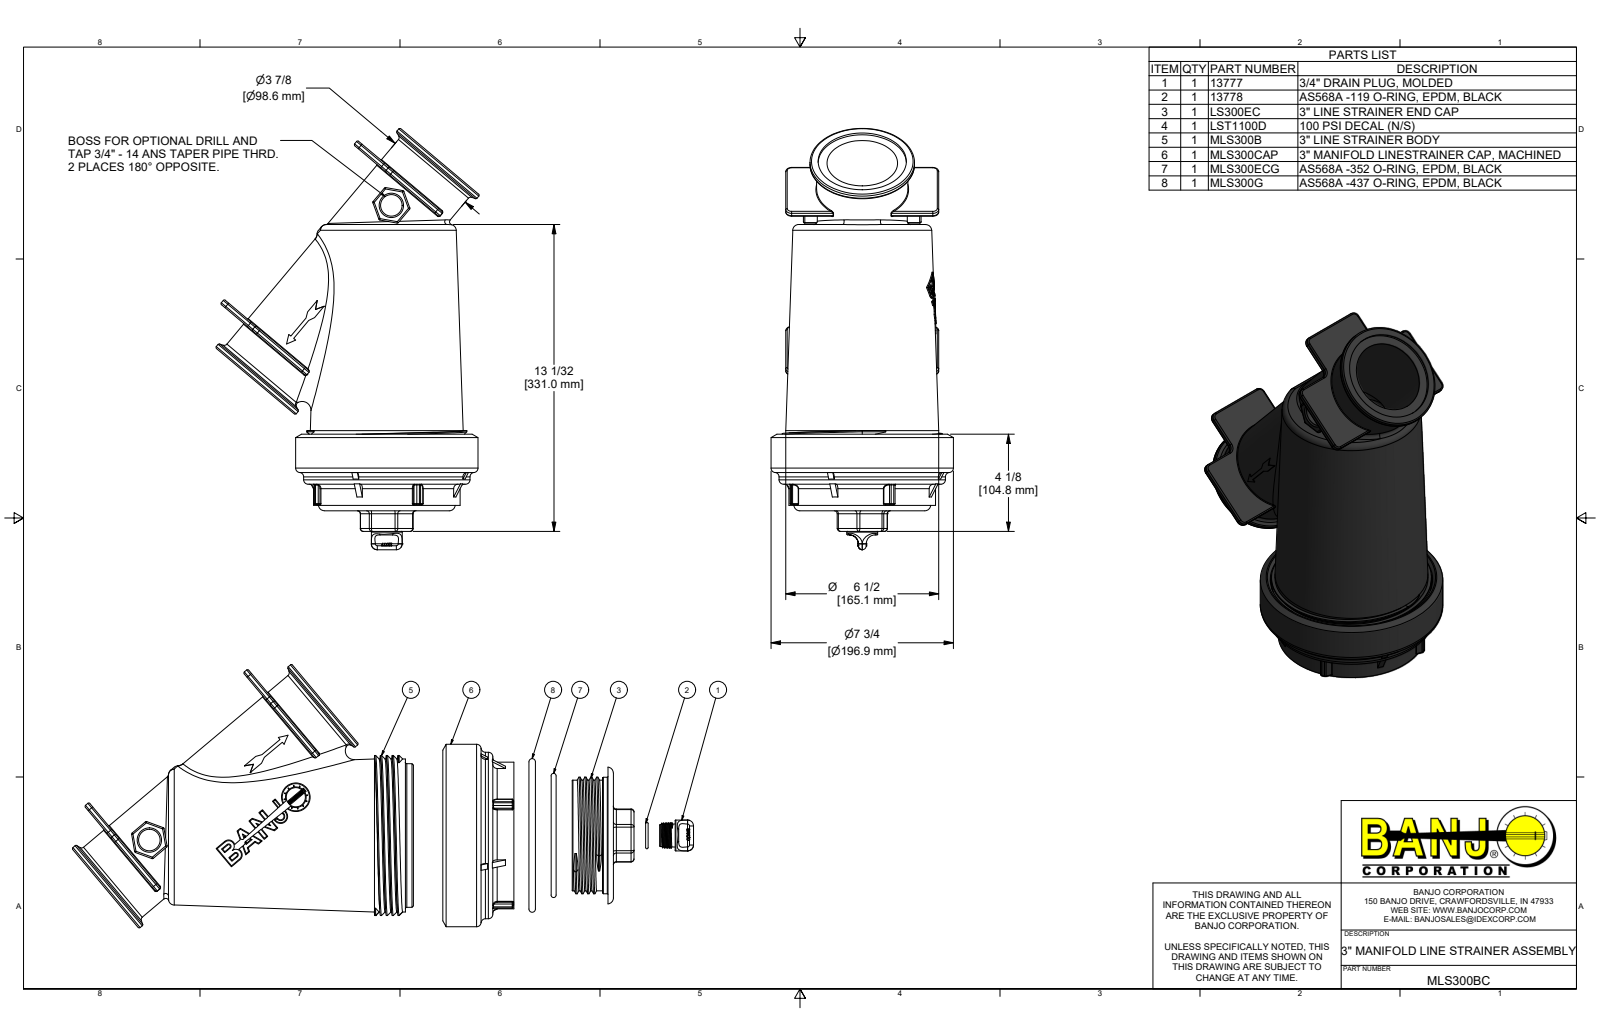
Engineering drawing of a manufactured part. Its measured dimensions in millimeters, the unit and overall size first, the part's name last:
Units: millimetres
Overall size (bounding box): 454.6 × 284.1 × 196.9
Round holes (diameter × count): ⌀95.3 ×2, ⌀17.8 ×1, ⌀20.8 ×1, ⌀23.1 ×1, ⌀29.3 ×1, ⌀76.2 ×1, ⌀101.6 ×1, ⌀109.7 ×1, ⌀109.7 ×1, ⌀120.1 ×1, ⌀127 ×1, ⌀137.5 ×1
Round bosses / shafts (diameter × count): ⌀112.8 ×2, ⌀98.6 ×2, ⌀196.9 ×1, ⌀179.6 ×1, ⌀172.7 ×1, ⌀165.1 ×1, ⌀158.2 ×1, ⌀154.9 ×1
Partial cylindrical surfaces — rounded edges, fillets, slot ends (radius × count): R1.5 ×46, R0.8 ×32, R3.2 ×18, R6.4 ×17, R0.5 ×8, R2.3 ×8, R0.4 ×6, R1.8 ×2
Main face-to-face distances: 5.8, 6.4, 223.9, 217.5, 230.3, 223.9, 6.4, 43.5, 261, 9.4
Hole centre spacings: 164.8
Volume: 2 997 000 mm³ · Surface area: 665 800 mm²
Bodies: 7 solids, 1046 faces (426 planar, 268 cylindrical, 352 other)
Part name (STEP PRODUCT): MLS300BC; MLS300B; MLS300G; MLS300ECG (+6 more)
STEP written by: Autodesk Inventor 2022 (AUTOMOTIVE_DESIGN)
